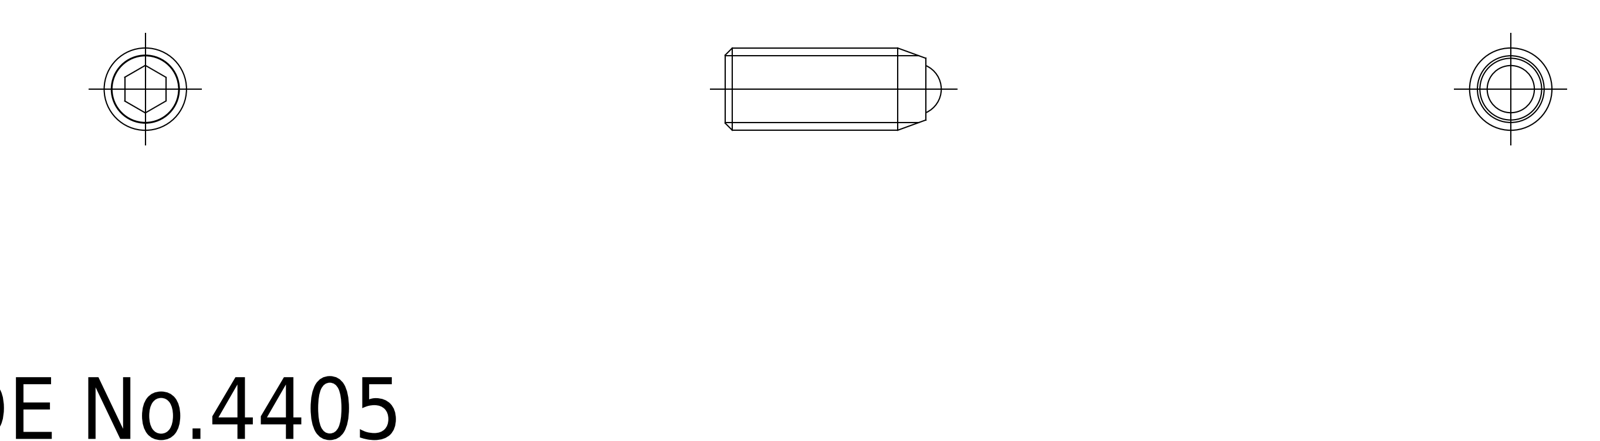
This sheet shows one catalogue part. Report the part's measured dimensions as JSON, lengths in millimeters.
{"part_name": "ball; SCSS_M4_10_R_18681_36", "step_written_by": "CADfix (AUTOMOTIVE_DESIGN)", "units": "millimeters", "bodies": {"solids": 2, "faces": 20, "planar": 0, "cylindrical": 0, "other": 20}, "overall_size": [10.5, 4, 4], "volume_mm3": 104, "surface_area_mm2": 198}
